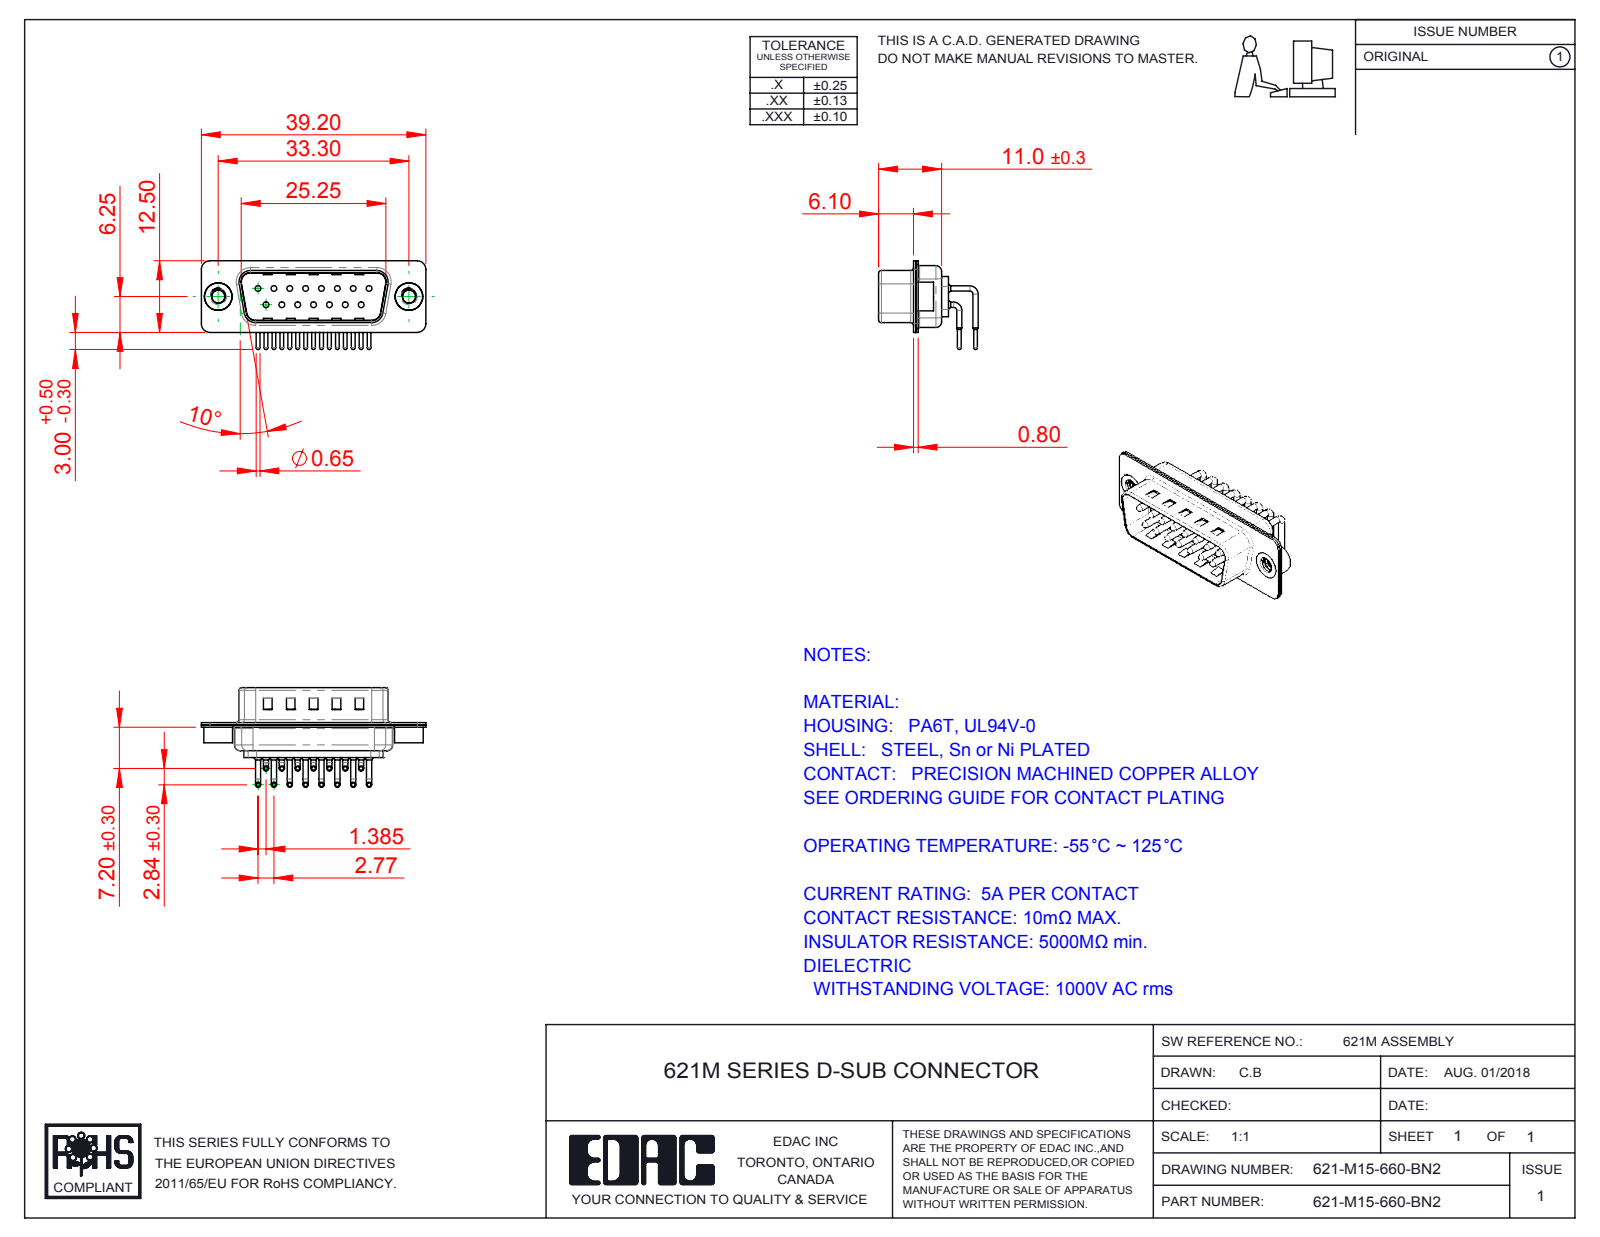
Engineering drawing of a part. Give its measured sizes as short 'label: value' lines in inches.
name: 621M Shell Front_15 Contacts; 621M Housing_15 Contacts; 621M Contact Row 2; 621M Contact Row 1 (+3 more)
written by: SolidWorks 2016 (CONFIG_CONTROL_DESIGN)
unit: in
bodies: 20 solids, 1990 faces (1099 planar, 673 cylindrical, 218 other)
size: 1.543 × 0.685 × 0.61
volume: 0.118 in³; area: 8.156 in²
holes: 15× ⌀0.039, 15× ⌀0.067, 15× ⌀0.079, 2× ⌀0.089, 2× ⌀0.157, 2× ⌀0.189
bosses: 30× ⌀0.035, 15× ⌀0.059, 15× ⌀0.026, 2× ⌀0.197, 2× ⌀0.193
rounds: 16× R0.059, 15× R0.04, 12× R0.079, 8× R0.02, 8× R0.063, 4× R0.01, 4× R0.024, 4× R0.026
face distances: 0.016, 0.033, 0.376, 0.343, 0.049, 0.409, 0.031, 0.059, 0.014, 0.075
hole spacings: 0.124, 0.109, 0.218, 0.327, 0.436, 0.198, 0.198, 0.294
